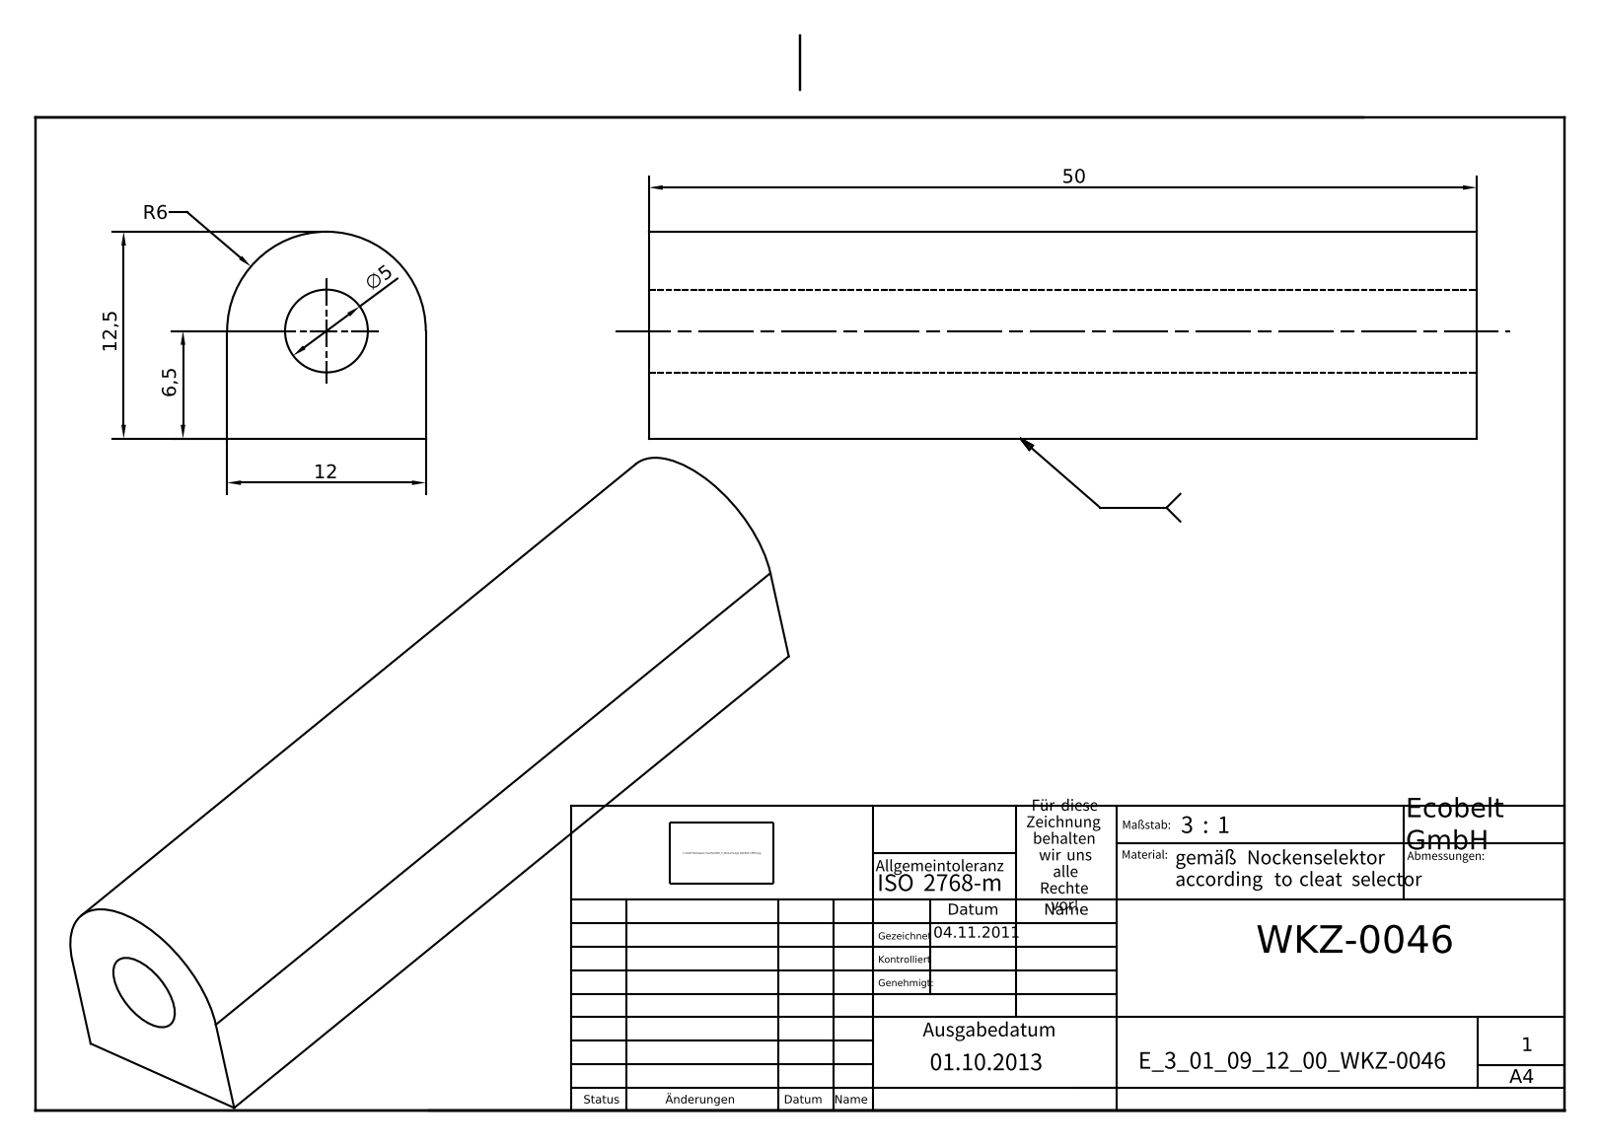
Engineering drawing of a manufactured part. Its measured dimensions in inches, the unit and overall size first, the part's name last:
Units: inches
Overall size (bounding box): 1.969 × 0.492 × 0.472
Round holes (diameter × count): ⌀0.197 ×1
Partial cylindrical surfaces — rounded edges, fillets, slot ends (radius × count): R0.236 ×1
Main face-to-face distances: 0.472, 1.969
Volume: 0.351 in³ · Surface area: 4.972 in²
Bodies: 1 solid, 7 faces (5 planar, 2 cylindrical, 0 other)
Part name (STEP PRODUCT): E_3_01_09_12_00_WKZ-0046
STEP written by: Autodesk Inventor 2025 (AUTOMOTIVE_DESIGN)
